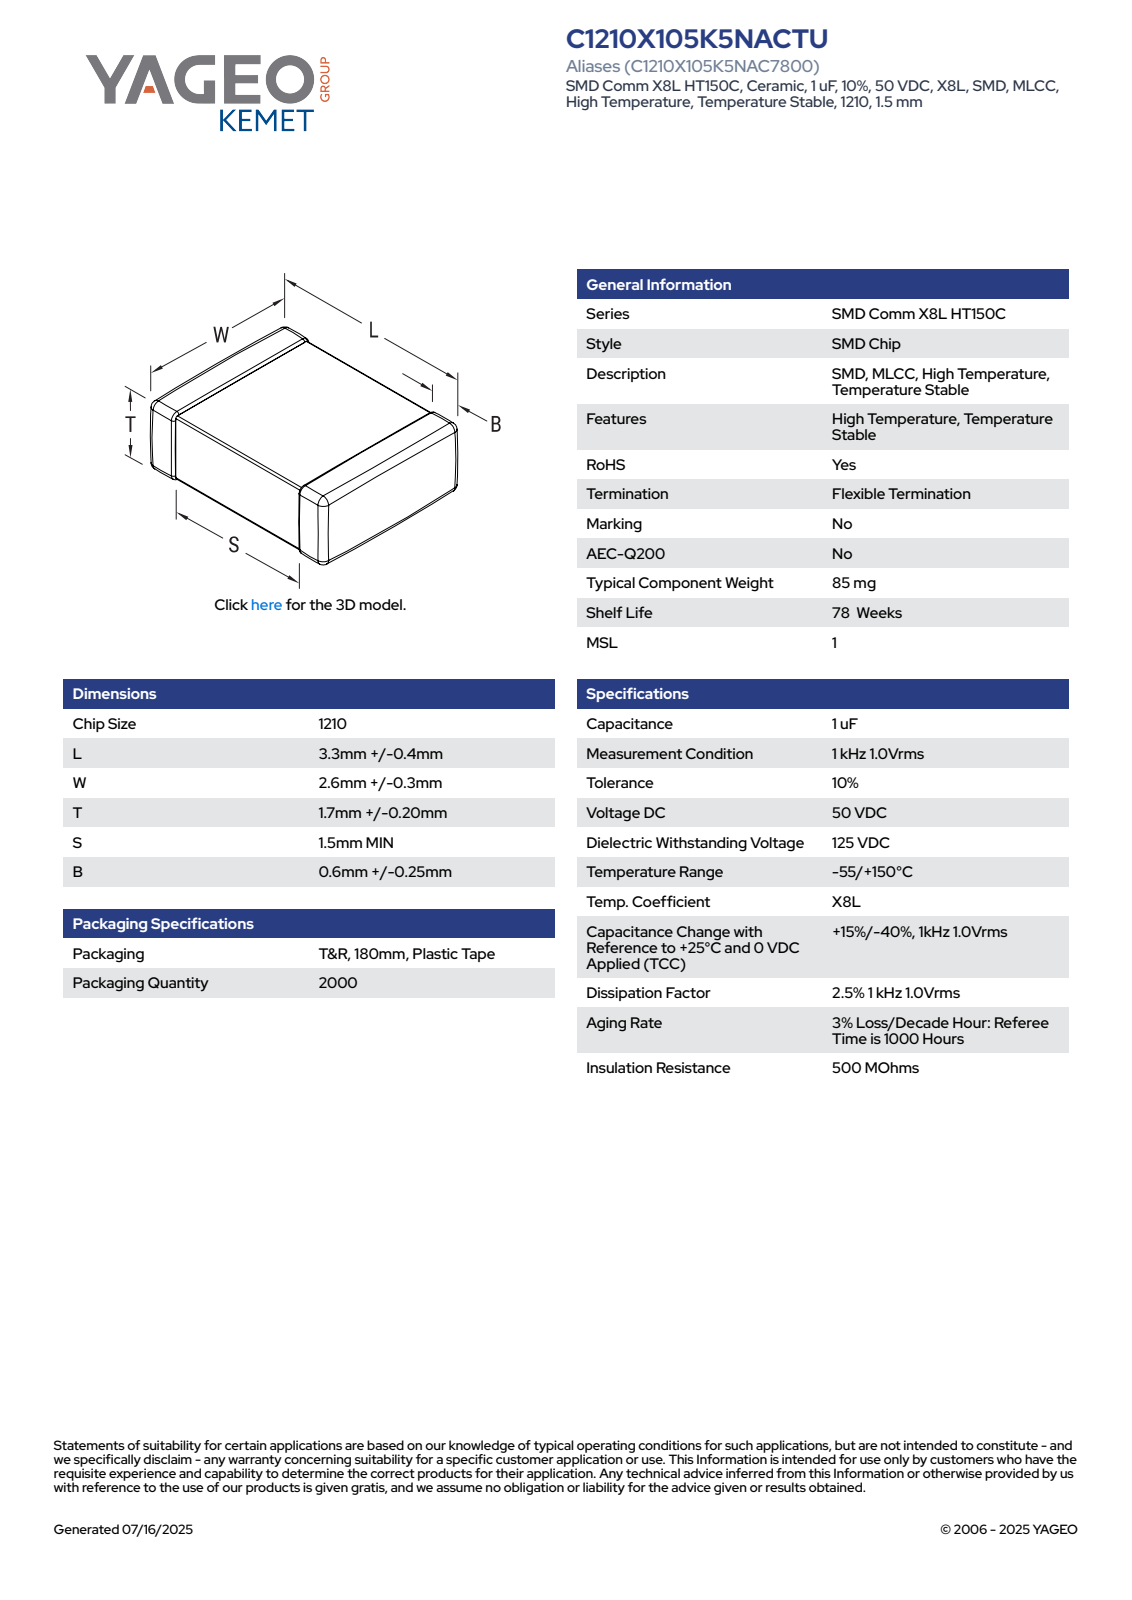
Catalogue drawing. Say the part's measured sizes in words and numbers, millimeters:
The part is named "CCS_CCSTDNOS_1210_L3.7W2.9T1.9B0.85". Its 3-D file was written by "SolidWorks 2014 (AUTOMOTIVE_DESIGN)". It is 4 solids with 125 faces: 71 planar, 38 cylindrical and 16 other. Overall it measures 3.7 by 2.9 by 1.9 millimeters. Its volume is 19 cubic millimeters and its surface area 46 square millimeters. The main face-to-face distances are 1.84, 1.78, 2.84, 3.7, 1.9, 2.78, 2.9, 1.4, 1.5, 1.34.
